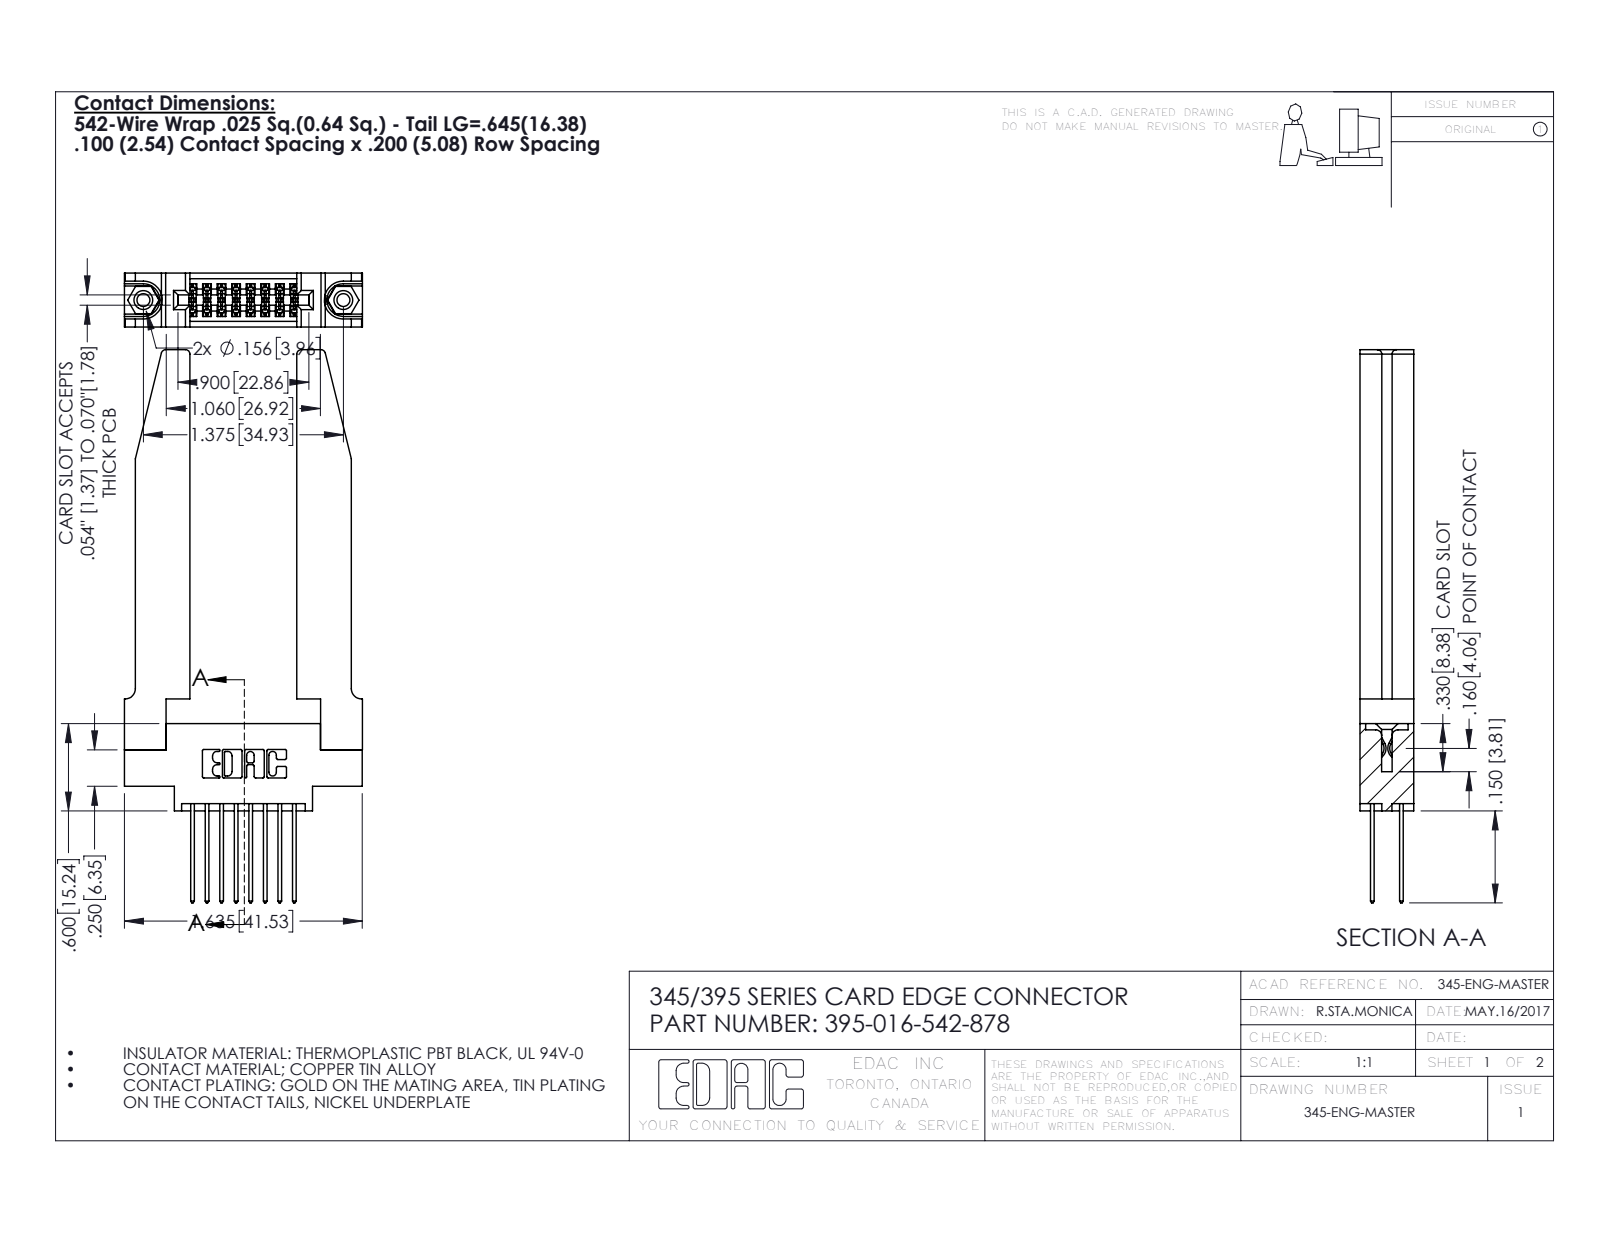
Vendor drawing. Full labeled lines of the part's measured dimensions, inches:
Part name (STEP PRODUCT): 345-250-001_345-250-001-102; 345 Part_0.170 Offset - 0.156 Dia-TH; 345-220-078_345-220-078; 395-016-542-878 (+1 more)
STEP written by: SolidWorks 2016 (CONFIG_CONTROL_DESIGN)
Units: inches
Bodies: 21 solids, 1164 faces (754 planar, 358 cylindrical, 52 other)
Overall size (bounding box): 3.802 × 1.636 × 0.37
Volume: 0.699 in³ · Surface area: 18.78 in²
Round holes (diameter × count): ⌀0.089 ×2, ⌀0.125 ×2, ⌀0.156 ×2, ⌀0.064 ×1
Round bosses / shafts (diameter × count): ⌀0.155 ×2
Partial cylindrical surfaces — rounded edges, fillets, slot ends (radius × count): R0.006 ×24, R0.01 ×22, R0.01 ×16, R0.03 ×8, R0.007 ×6, R0.031 ×6, R0.026 ×3, R0.014 ×2
Main face-to-face distances: 0.37, 0.072, 0.298, 0.148, 0.15, 0.22, 0.077, 0.735, 0.123, 0.098
Hole centre spacings: 0.27, 1.144, 1.375
